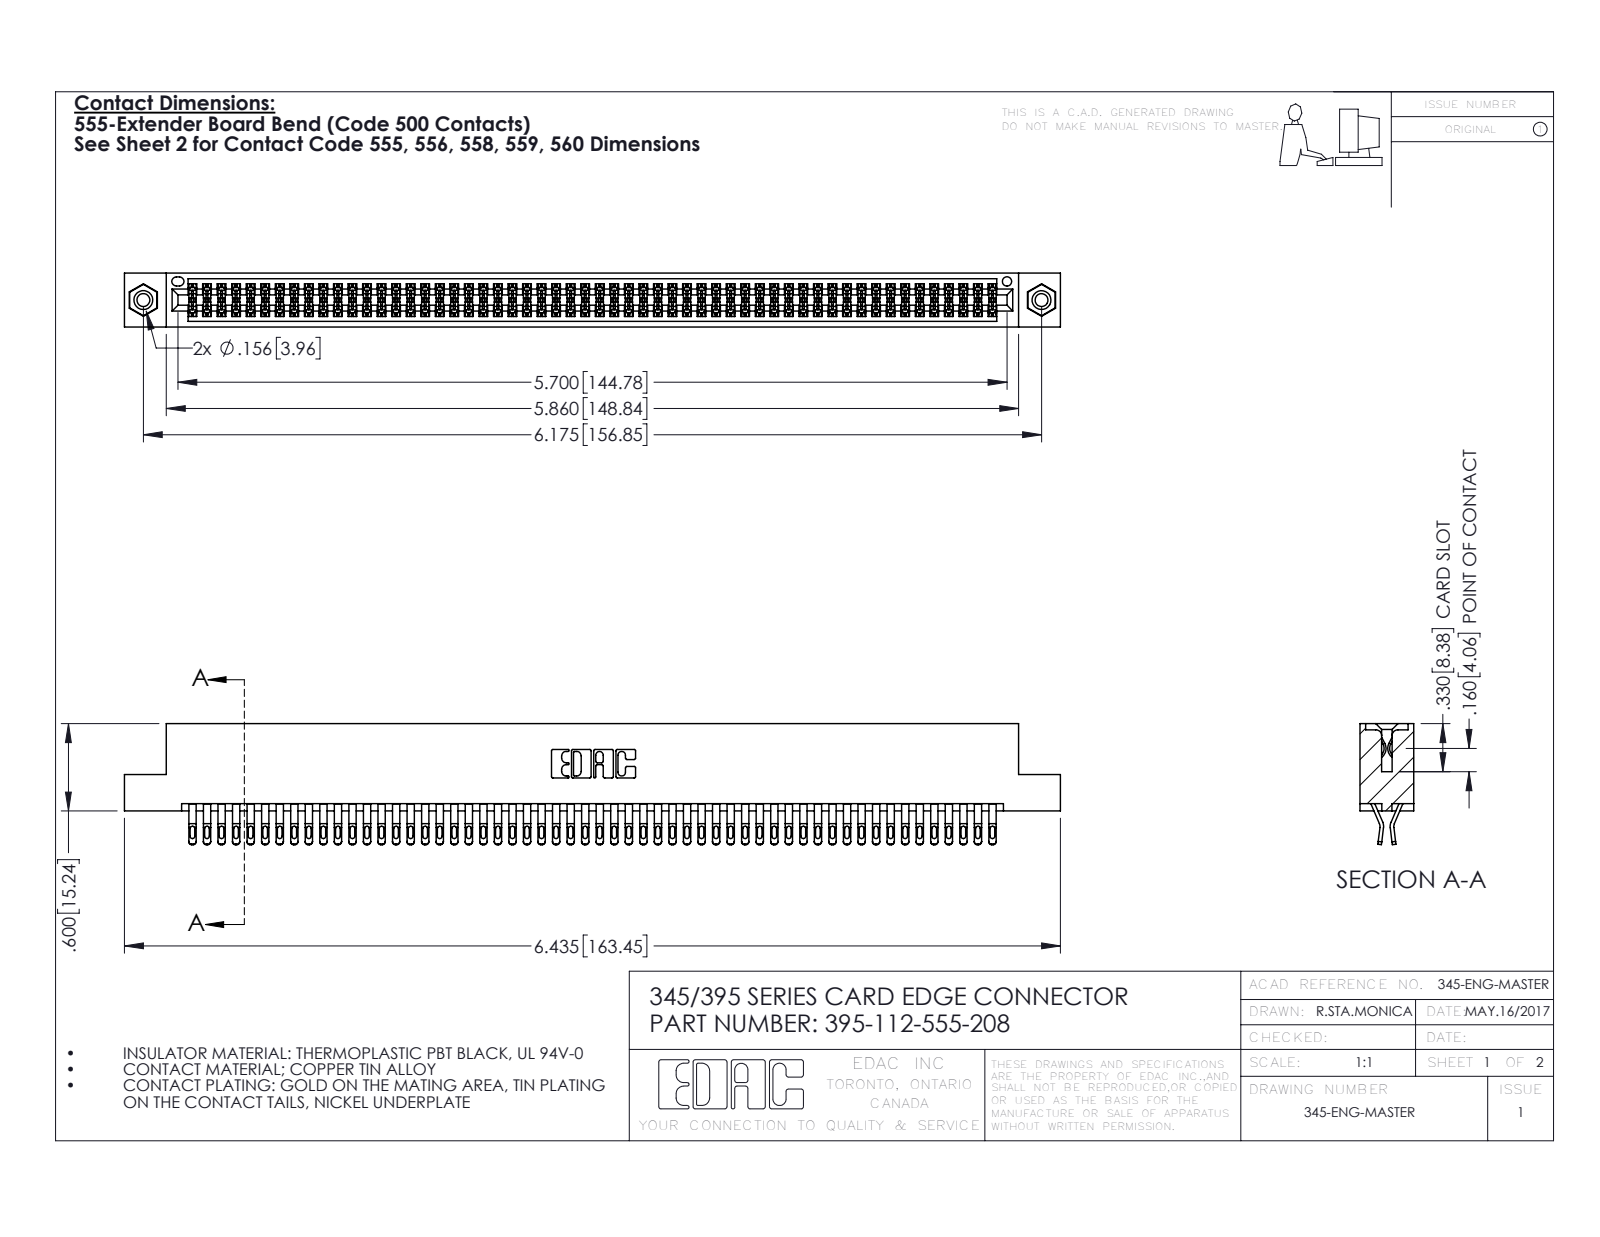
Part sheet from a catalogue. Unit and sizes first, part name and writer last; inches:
Units: inches
Overall size (bounding box): 6.435 × 0.832 × 0.37
Round holes (diameter × count): ⌀0.089 ×2, ⌀0.125 ×2, ⌀0.156 ×2, ⌀0.064 ×1
Round bosses / shafts (diameter × count): ⌀0.155 ×2
Partial cylindrical surfaces — rounded edges, fillets, slot ends (radius × count): R0.016 ×280, R0.02 ×224, R0.006 ×168, R0.01 ×22, R0.007 ×6, R0.031 ×6, R0.026 ×3, R0.01 ×2
Main face-to-face distances: 0.072, 0.298, 0.025, 0.37, 0.2, 0.098, 0.272, 0.225, 0.175, 0.149
Hole centre spacings: 0.27, 5.939, 6.175
Volume: 0.996 in³ · Surface area: 39.6 in²
Bodies: 115 solids, 6458 faces (3584 planar, 2858 cylindrical, 16 other)
Part name (STEP PRODUCT): 345-250-001_345-250-003-102; 395-112-555-208; 345 Part_Flush Mounting Lugs - 0.156 Dia-TI; 345-292-001_555 Tail
STEP written by: SolidWorks 2016 (CONFIG_CONTROL_DESIGN)
